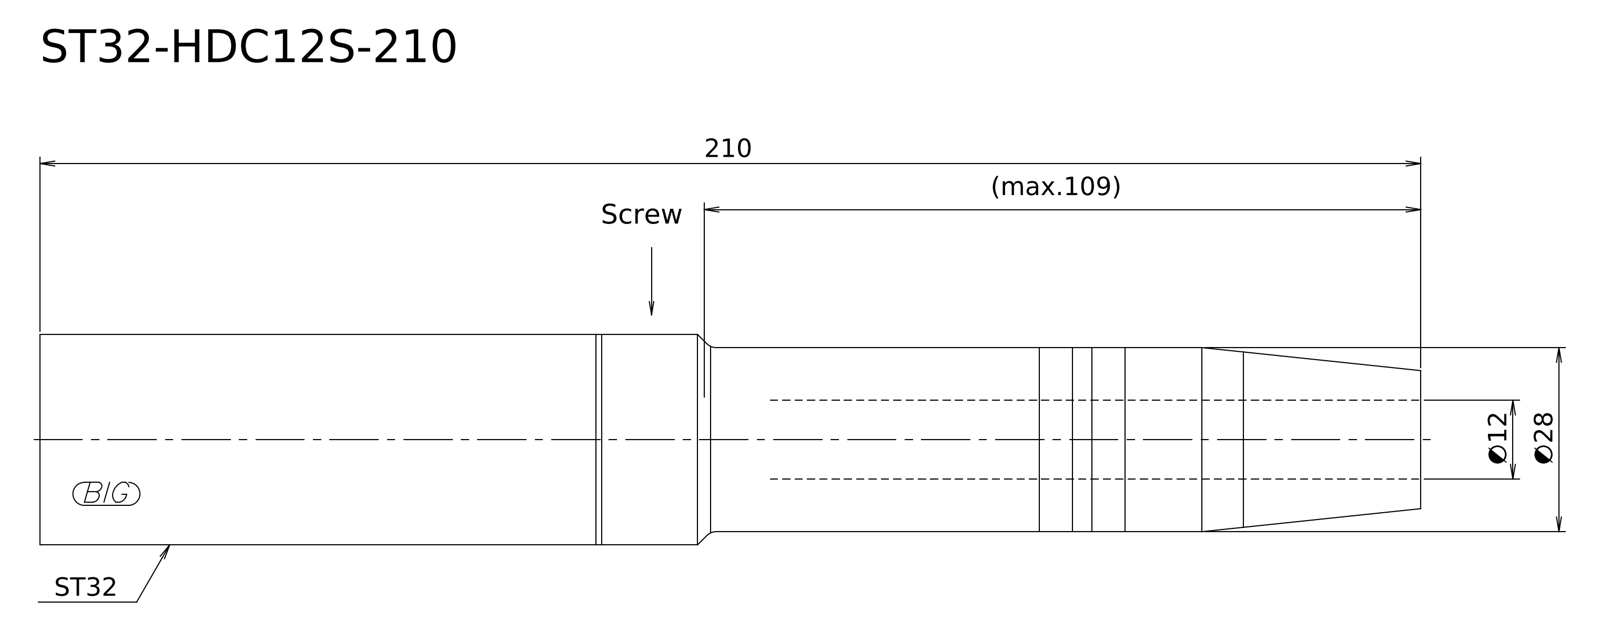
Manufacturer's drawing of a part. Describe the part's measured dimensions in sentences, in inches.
Its 3-D file was written by "Kubotek KeyCreator V8.5.1 (14335) (CONFIG_CONTROL_DESIGN)". It is 1 solid with 7 faces: 2 planar, 2 cylindrical and 3 other. Overall it measures 8.268 by 1.26 by 1.26 inches. Its volume is 8.767 cubic inches and its surface area 31.94 square inches. Round bosses or shafts: 1 of diameter 1.26, 1 of diameter 1.102. The main face-to-face distances are 8.268.
